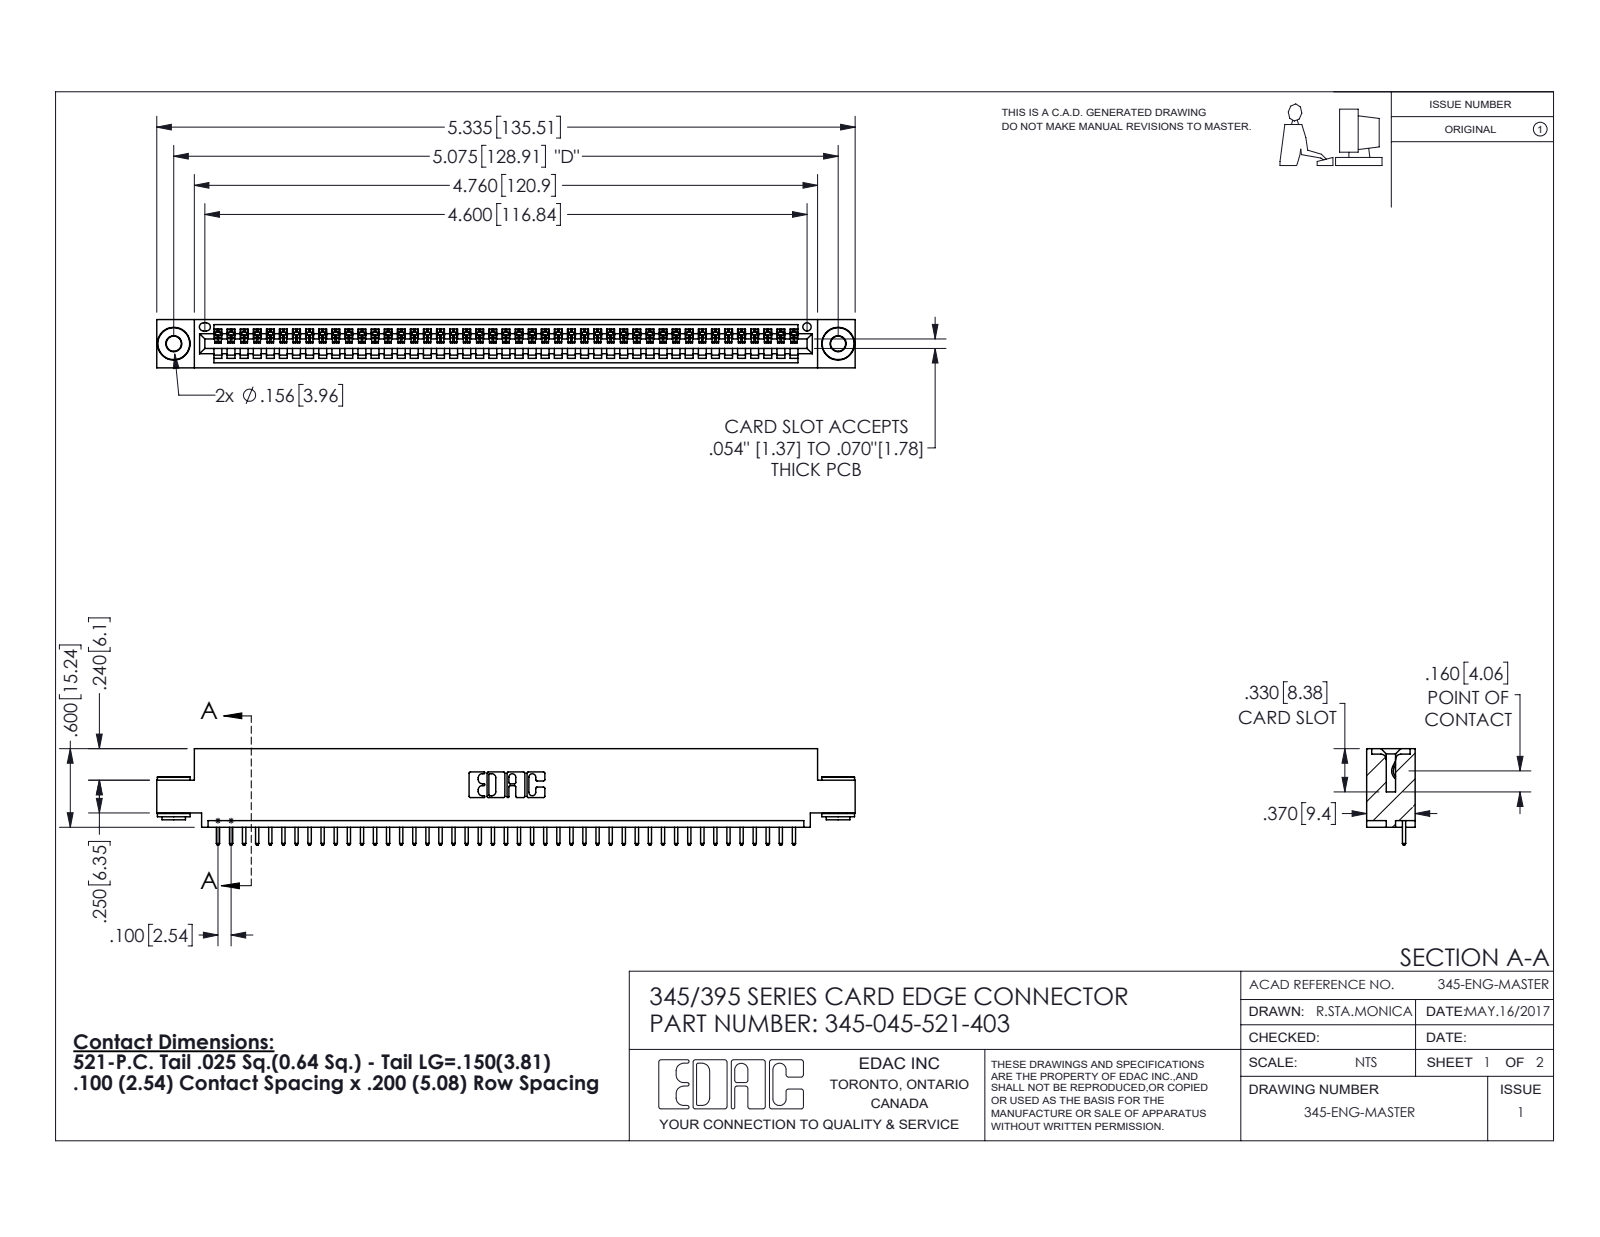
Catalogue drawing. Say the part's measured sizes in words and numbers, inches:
The part is named "345-292-001_345-293-121; 345 Part_0.110 Offset - 0.156 Dia-TH; 345-045-521-403; 345-250-002_345-250-002-102". Its 3-D file was written by "SolidWorks 2016 (CONFIG_CONTROL_DESIGN)". It is 48 solids with 2778 faces: 1894 planar, 876 cylindrical and 8 other. Overall it measures 5.335 by 0.737 by 0.37 inches. Its volume is 0.776 cubic inches and its surface area 25.93 square inches. Round holes: 2 of diameter 0.116, 2 of diameter 0.156, 1 of diameter 0.064. Round bosses or shafts: 2 of diameter 0.25, 2 of diameter 0.18, 2 of diameter 0.136. Partial cylindrical surfaces (rounded edges, fillets, slot ends): 90 of radius 0.006, 90 of radius 0.01, 22 of radius 0.01, 6 of radius 0.007, 6 of radius 0.031, 3 of radius 0.026, 2 of radius 0.031, 2 of radius 0.04. The main face-to-face distances are 0.072, 0.298, 0.37, 0.2, 0.025, 0.098, 0.272, 0.225, 0.149, 0.072. The hole center spacings are 0.27, 4.839, 5.075.
